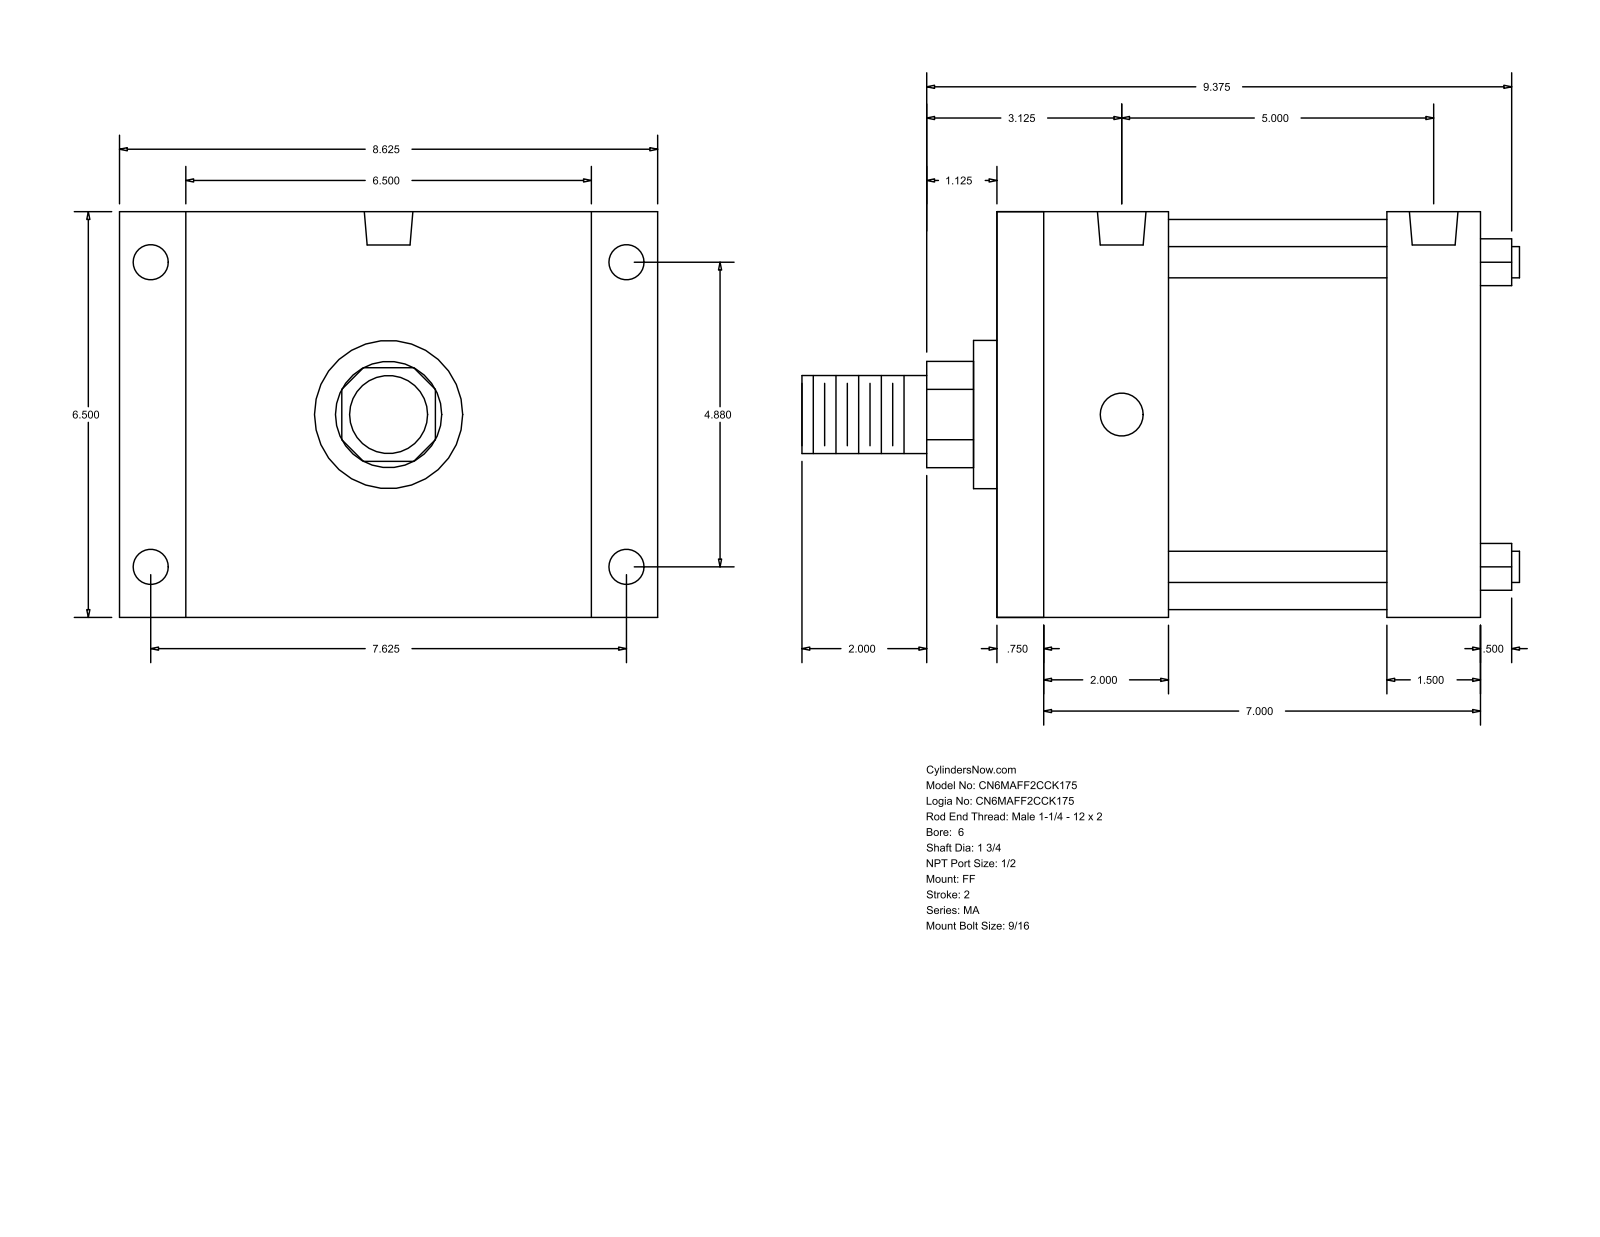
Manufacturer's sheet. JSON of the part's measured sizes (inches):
{"part_name": "MA_FF__0600_1.75", "step_written_by": "GSSL Pune (CONFIG_CONTROL_DESIGN)", "units": "inches", "bodies": {"solids": 0, "faces": 92, "planar": 64, "cylindrical": 28, "other": 0}, "overall_size": [11.5, 8.625, 6.5], "round_holes": [[0.563, 4], [0.687, 4], [0.778, 2]], "round_bosses_or_shafts": [[0.5, 4], [6.25, 1], [2.375, 1], [1.75, 1], [1.25, 1]], "partial_cylinders_radius": [[0.852, 1]], "face_to_face_distances": [6.5, 7.75, 0.75, 7, 2, 2.75, 5.5, 5, 6.25, 3.5], "hole_center_spacings": [4.88, 5, 7.625, 9.053]}
